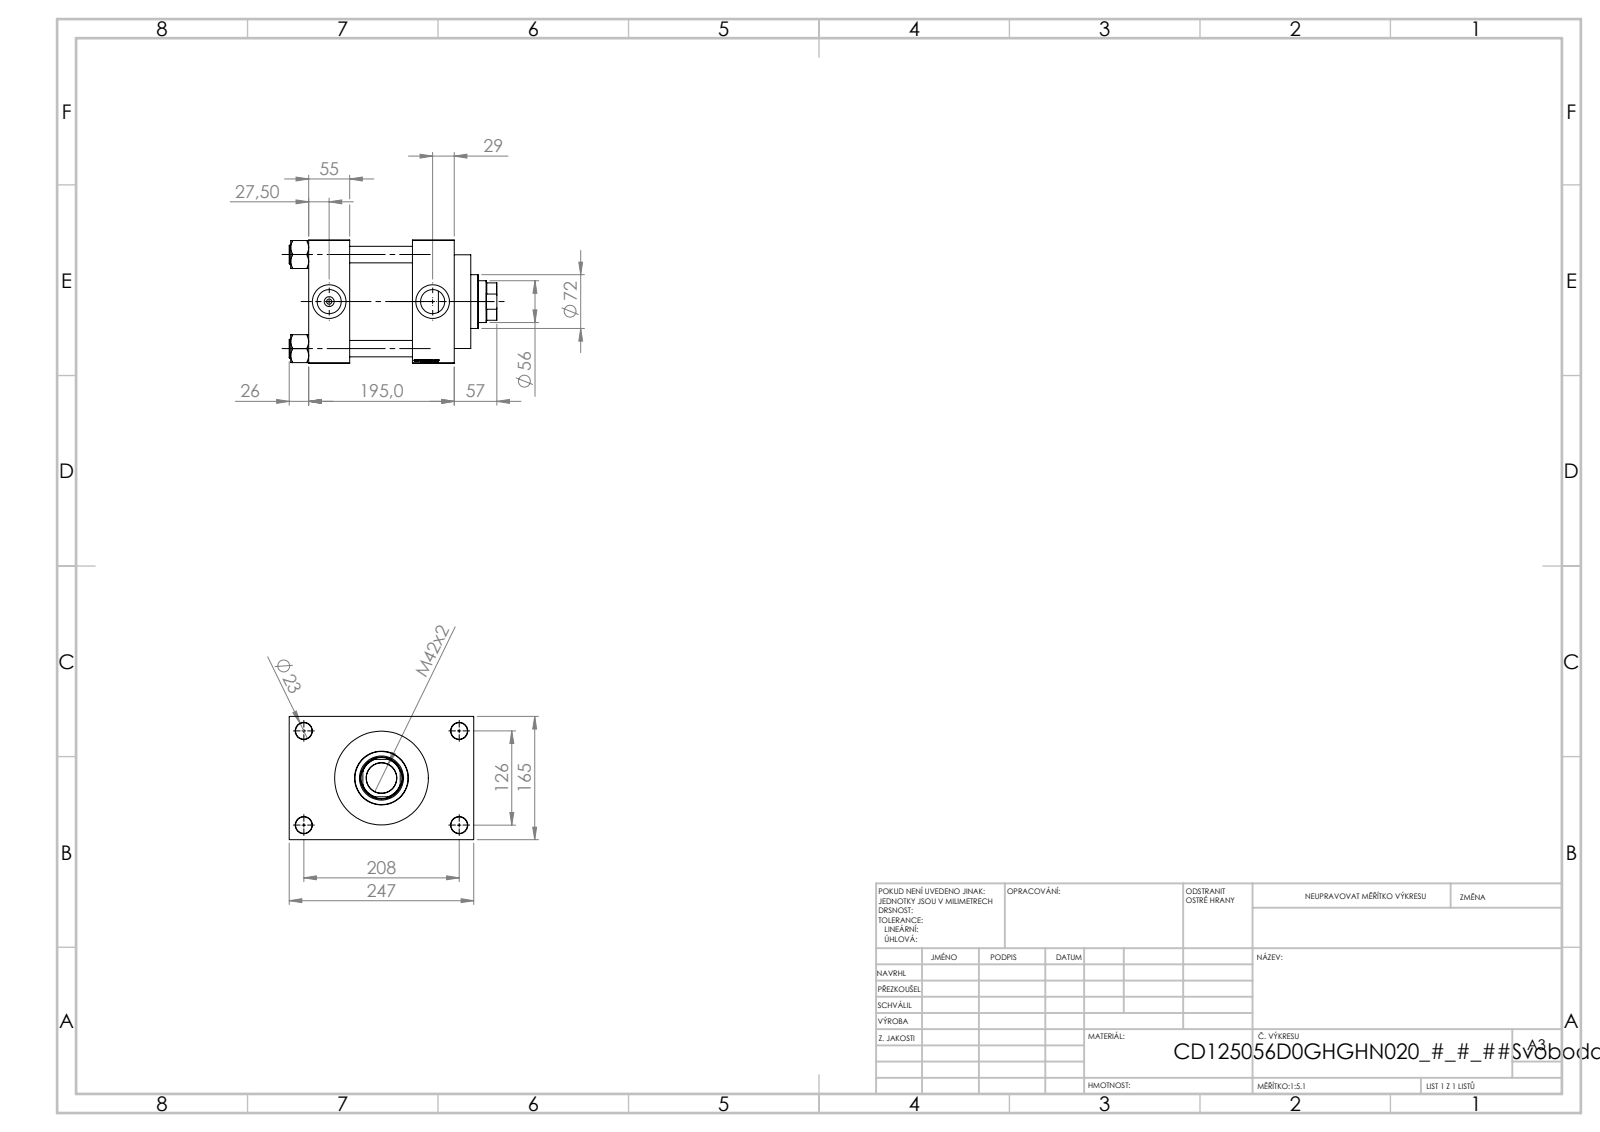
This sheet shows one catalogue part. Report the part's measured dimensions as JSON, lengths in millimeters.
{"part_name": "V215CD_VC_A; V215CD_D_TYCINKA; V215CD_NUT_M5_D; V215CD_VCP_D (+1 more)", "step_written_by": "SolidWorks 2019 (CONFIG_CONTROL_DESIGN)", "units": "millimeters", "bodies": {"solids": 11, "faces": 1148, "planar": 544, "cylindrical": 86, "other": 518}, "overall_size": [278, 247, 165], "volume_mm3": 4924000, "surface_area_mm2": 534057, "round_holes": [[22, 8], [7, 2], [32.24, 2], [45, 2], [40.5, 1], [56, 1], [59, 1], [96, 1], [125, 1], [125.5, 1]], "round_bosses_or_shafts": [[25, 4], [131, 1], [72, 1]], "partial_cylinders_radius": [[27, 1]], "face_to_face_distances": [165, 84, 55, 139, 56, 195, 140, 41, 206, 173.74], "hole_center_spacings": [41.05, 89.02, 121.59, 125.9, 132.47, 166.95, 209.13, 126]}
